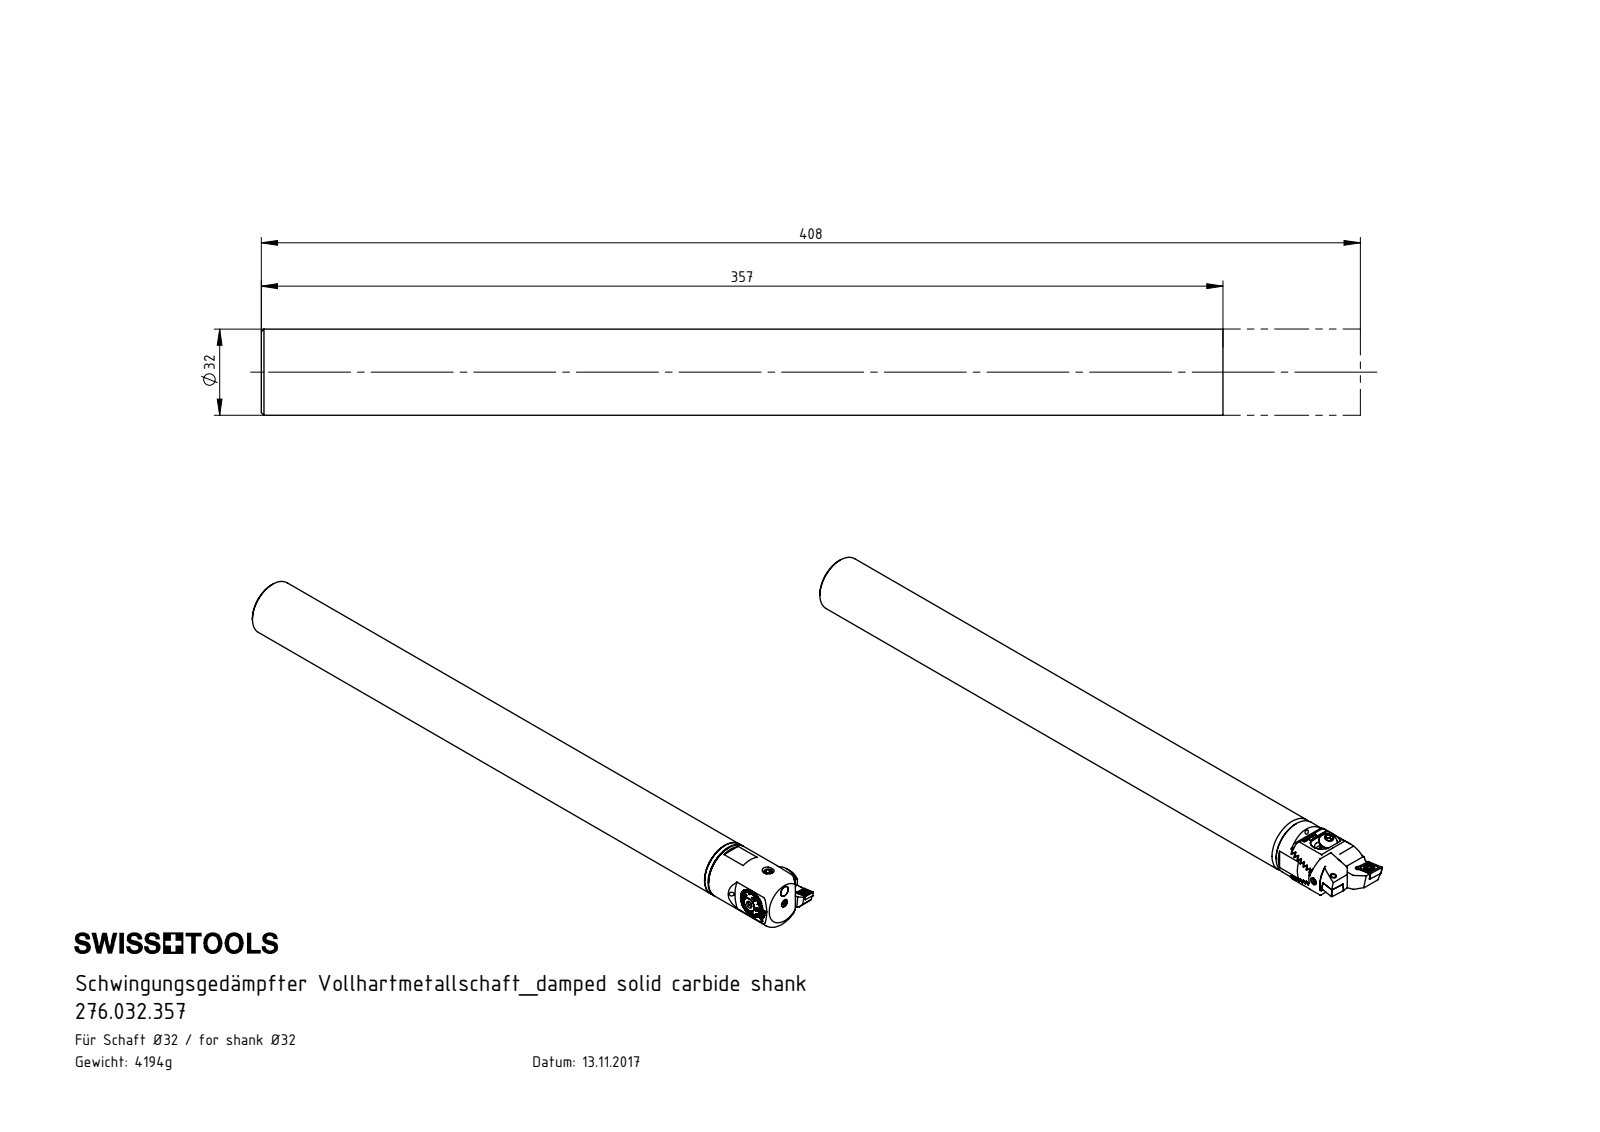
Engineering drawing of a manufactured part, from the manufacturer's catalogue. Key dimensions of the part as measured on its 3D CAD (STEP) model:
Part name (STEP PRODUCT): 276.032.357; HP5-ER1.019.036_A; HP5-Z32.040.051_fr Zeichnung; Z32-WCB.001.021 (+8 more)
STEP written by: SolidWorks 2017 (CONFIG_CONTROL_DESIGN)
Units: millimetres
Bodies: 16 solids, 976 faces (446 planar, 238 cylindrical, 292 other)
Overall size (bounding box): 408 × 40 × 32
Volume: 303 486 mm³ · Surface area: 63 883 mm²
Round holes (diameter × count): ⌀2.5 ×5, ⌀3.3 ×4, ⌀1.6 ×2, ⌀2 ×2, ⌀4.4 ×2, ⌀5 ×2, ⌀6.1 ×2, ⌀6.4 ×2, ⌀6.8 ×2, ⌀3.5 ×1, ⌀4.2 ×1, ⌀10.2 ×1
Round bosses / shafts (diameter × count): ⌀4 ×4, ⌀10.5 ×2, ⌀10.2 ×2, ⌀6 ×2, ⌀5.25 ×2, ⌀32 ×1, ⌀3 ×1, ⌀2.2 ×1
Partial cylindrical surfaces — rounded edges, fillets, slot ends (radius × count): R0.5 ×16, R0.2 ×14, R0.2 ×12, R0.34 ×12, R0.59 ×12, R2 ×4, R3.3 ×4, R6 ×4
Main face-to-face distances: 2.38, 4.76, 7.14, 3, 357, 360, 9.52, 36, 39, 321
Hole centre spacings: 6.07, 6.19, 24.22, 24.33, 28.65, 9, 9.01, 17.39
